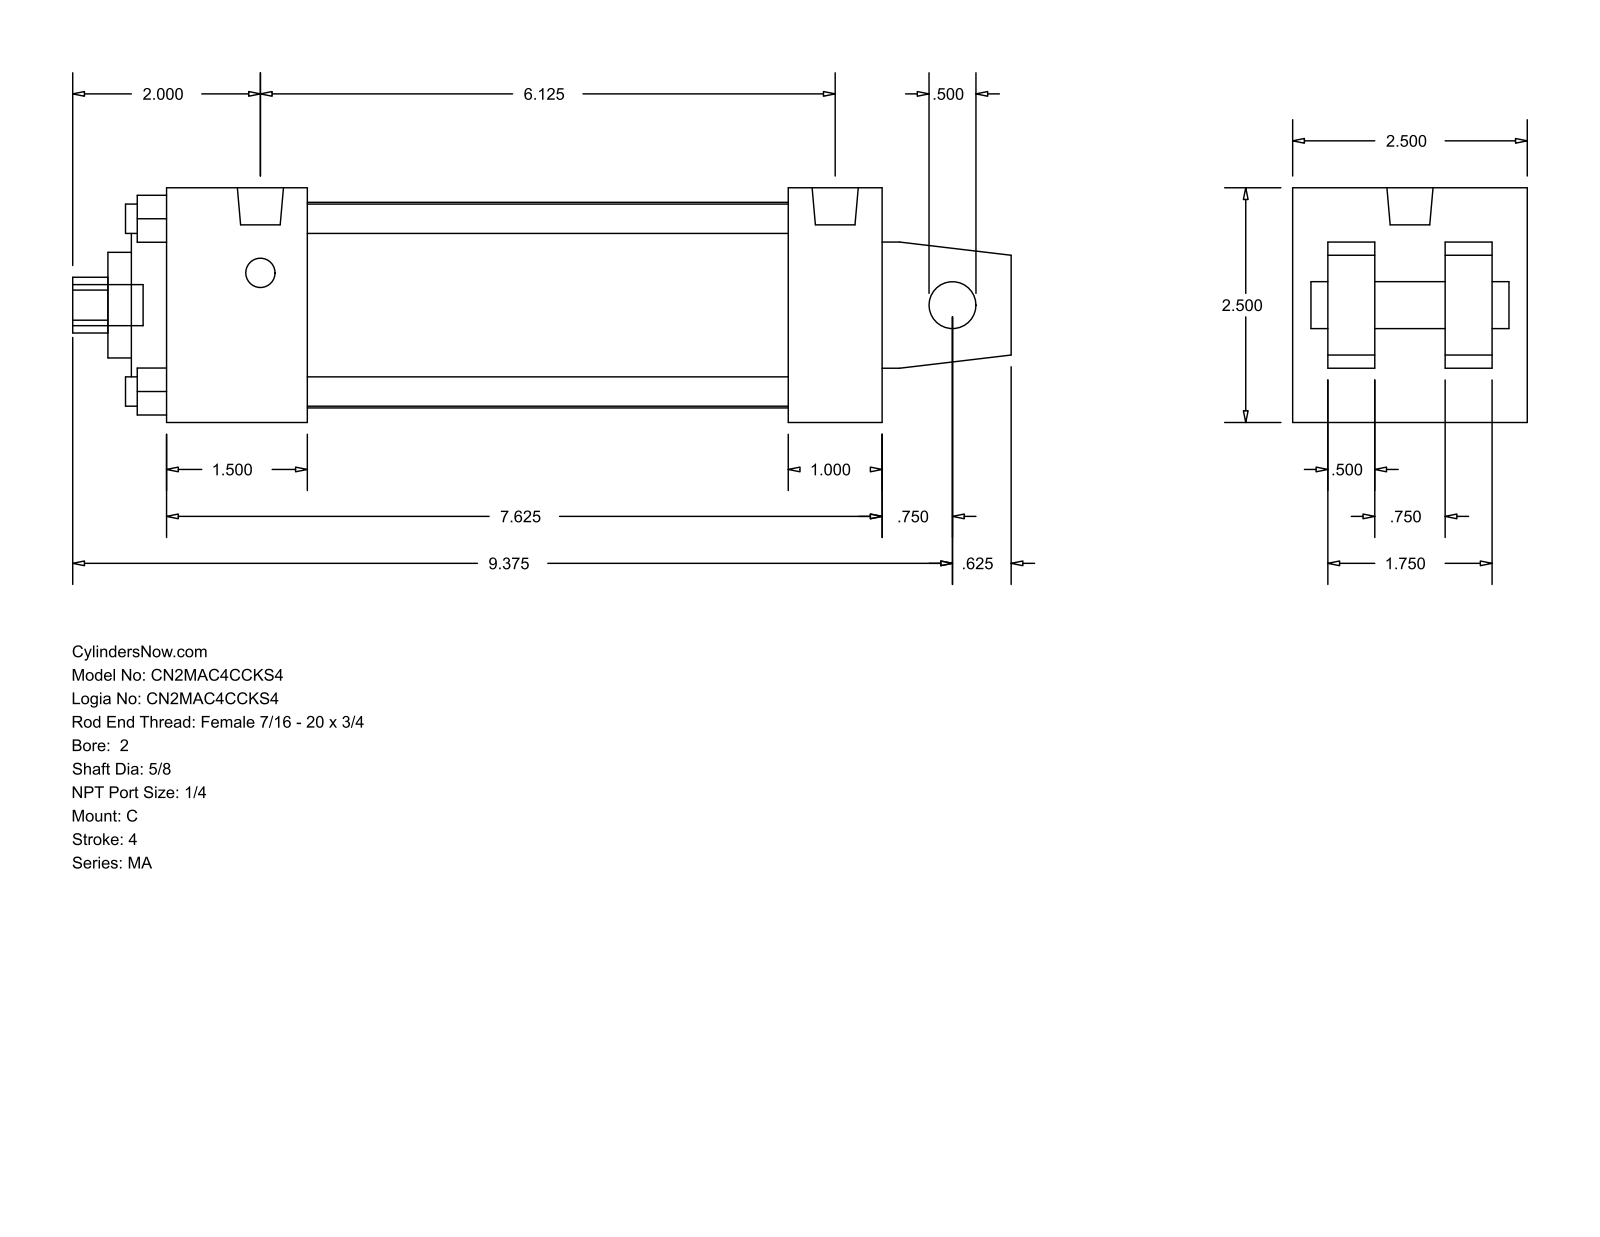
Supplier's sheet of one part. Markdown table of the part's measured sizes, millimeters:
| quantity | value |
| --- | --- |
| part name | MA_C__0200_0.625 |
| STEP written by | GSSL Pune (CONFIG_CONTROL_DESIGN) |
| units | millimeters |
| bodies | 0 solids, 105 faces (77 planar, 28 cylindrical, 0 other) |
| overall size | 254 × 63.5 × 63.5 |
| round holes (diameter × count) | 7.94 × 4, 12.7 × 1, 15.88 × 1, 28.57 × 1, 50.8 × 1, 55.63 × 1 |
| round bosses / shafts (diameter × count) | 7.94 × 4, 12.49 × 2, 11.11 × 1 |
| partial cylindrical surfaces (radius × count) | 7.54 × 1 |
| main face-to-face distances | 63.5, 9.52, 12.7, 22.22, 41.28, 53.98, 31.76, 38.1, 193.67, 155.57 |
| hole center spacings | 33.05, 46.74, 66.1 |
